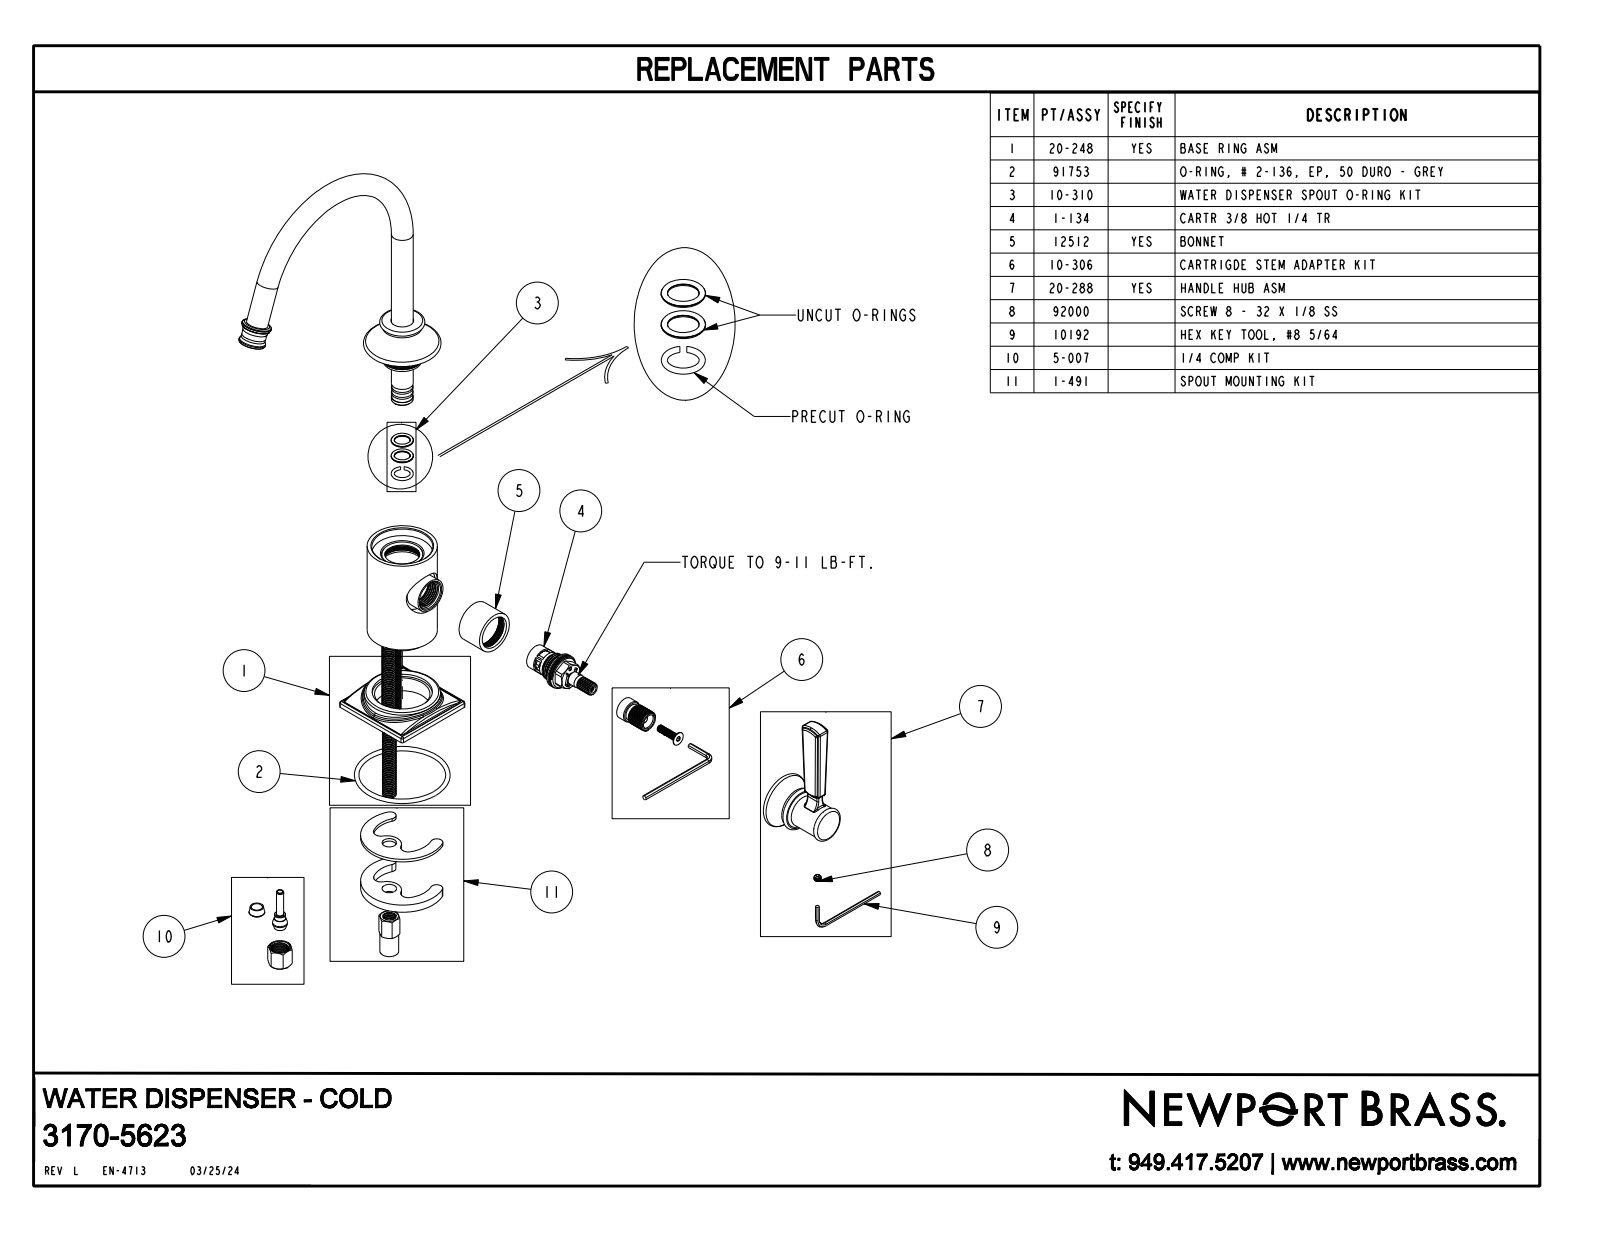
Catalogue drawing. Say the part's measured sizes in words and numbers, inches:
The part is named "3170-5623". Its 3-D file was written by "CREO PARAMETRIC BY PTC INC, 2018400 (CONFIG_CONTROL_DESIGN)". It is 1 solid with 238 faces: 25 planar, 57 cylindrical and 156 other. Overall it measures 9.373 by 6.053 by 3.59 inches. Its volume is 10.62 cubic inches and its surface area 52.72 square inches. Round holes: 1 of diameter 1. Round bosses or shafts: 2 of diameter 0.5, 1 of diameter 1.75, 1 of diameter 1.61, 1 of diameter 0.97, 1 of diameter 0.76. Partial cylindrical surfaces (rounded edges, fillets, slot ends): 16 of radius 0.04, 10 of radius 0.02, 6 of radius 0.03, 4 of radius 0.037, 2 of radius 0.33, 1 of radius 0.45, 1 of radius 0.57. The main face-to-face distances are 3.418, 2.05, 1.49, 2.1, 3.59, 0.05, 1.54, 0.067, 1.982, 0.425.
